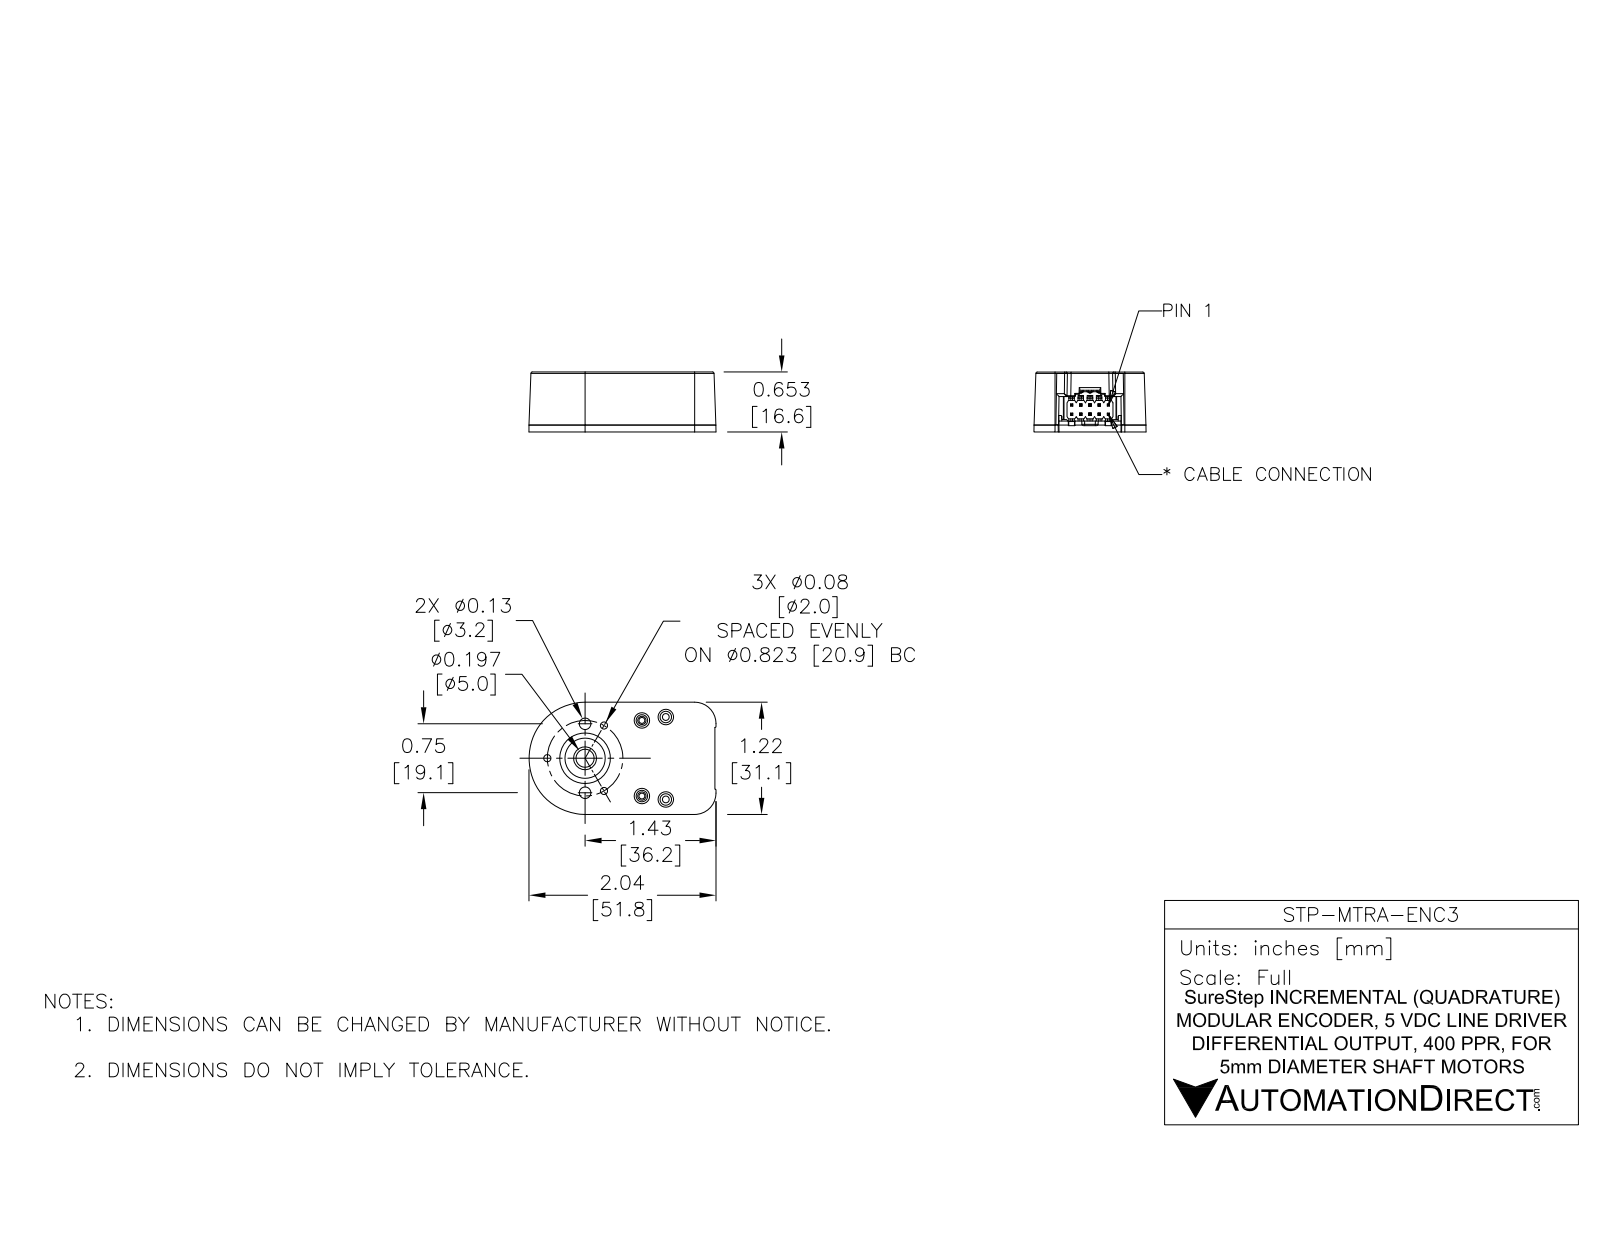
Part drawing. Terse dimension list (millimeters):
name: STP-MTRA-ENC3
written by: SolidWorks 2017 (AUTOMOTIVE_DESIGN)
unit: mm
bodies: 29 solids, 1688 faces (782 planar, 424 cylindrical, 482 other)
size: 51.8 × 31.1 × 16.6
volume: 12 500 mm³; area: 13 370 mm²
holes: 5× ⌀0.8, 4× ⌀2.3, 4× ⌀3.3, 3× ⌀2, 2× ⌀3.2, 1× ⌀2.4, 1× ⌀5
bosses: 5× ⌀2, 4× ⌀4.7, 4× ⌀4.1, 4× ⌀2.4, 3× ⌀2.8, 2× ⌀5, 1× ⌀13.2, 1× ⌀12.4
rounds: 46× R0.6, 37× R0.4, 14× R0.1, 14× R0.2, 10× R0.5, 8× R0.8, 6× R0.4, 6× R0.8
face distances: 16.6, 1.5, 2.9, 3.4, 13.7, 10.3, 13.2, 1.9, 2.5, 1.9
hole spacings: 2.5, 5.1, 10.4, 18.1, 5.3, 6.7, 7.6, 9.5
